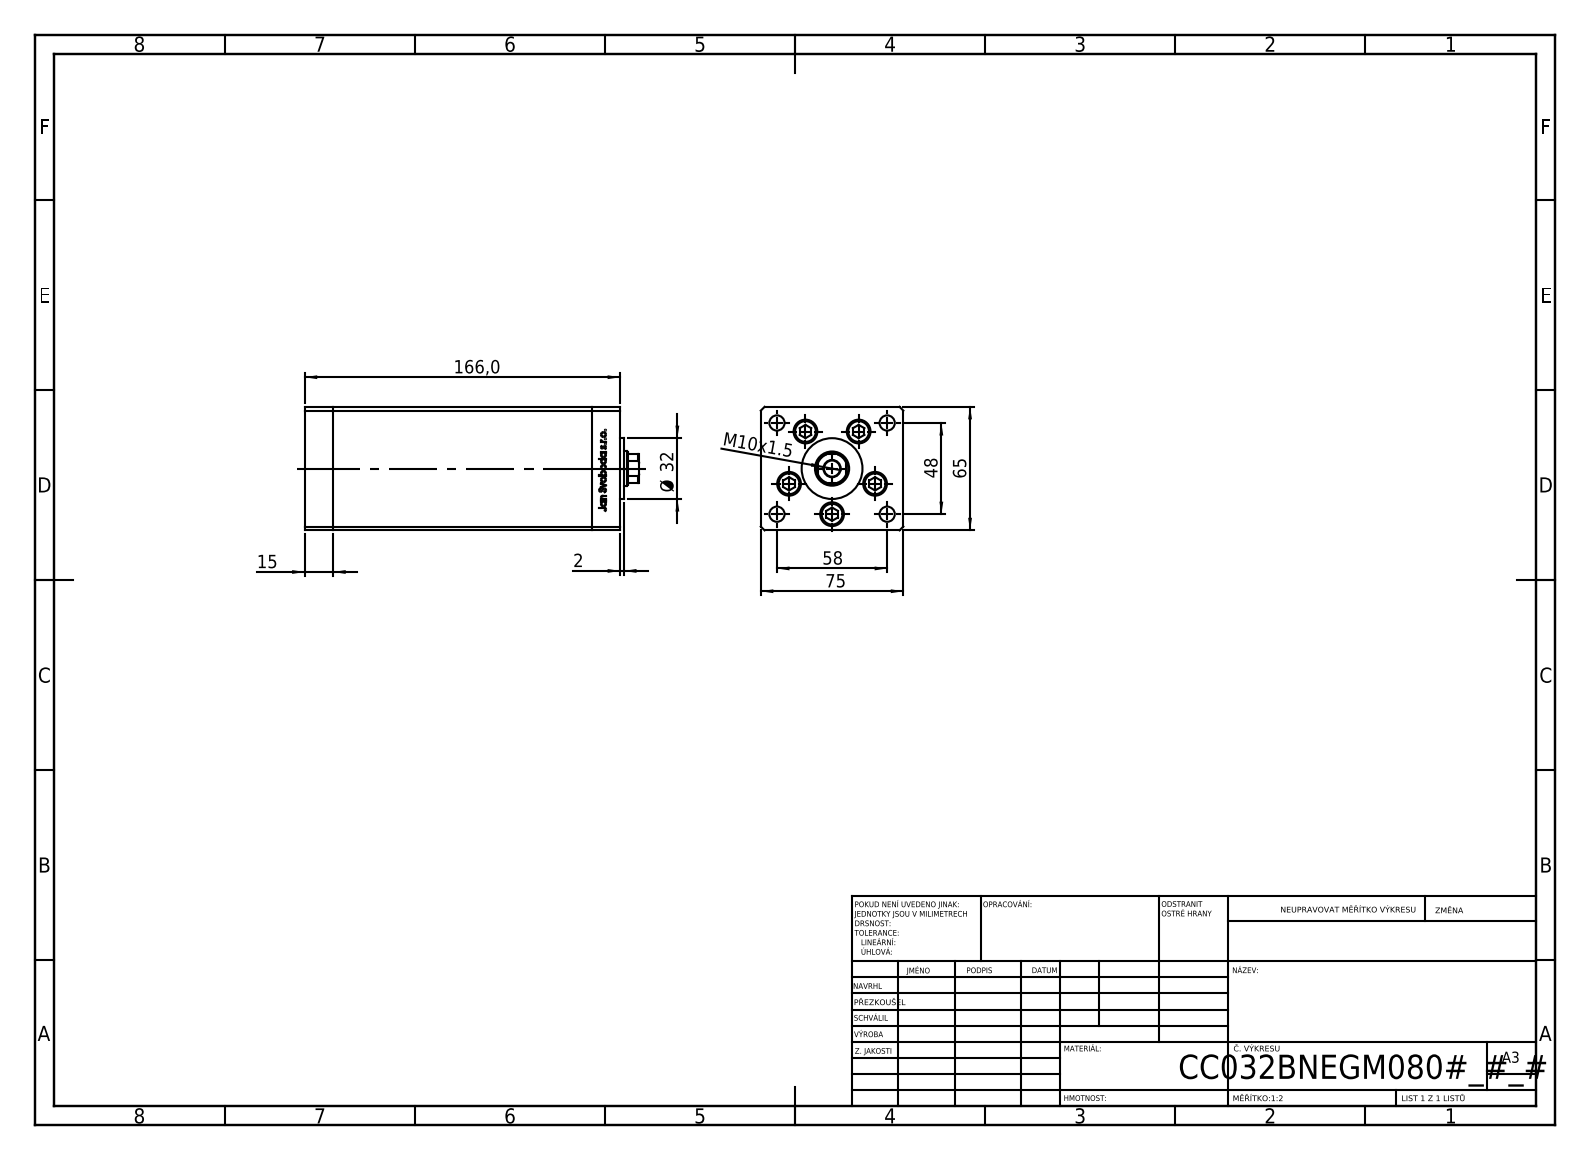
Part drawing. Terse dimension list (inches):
name: V220C_B MIDDLE; V220C_VC_B; V220C BACK_B; V220C_FRONT_B (+1 more)
written by: SolidWorks 2019 (CONFIG_CONTROL_DESIGN)
unit: in
bodies: 14 solids, 1183 faces (462 planar, 147 cylindrical, 574 other)
size: 6.929 × 2.953 × 2.559
volume: 44.09 in³; area: 197.4 in²
holes: 5× ⌀0.354, 5× ⌀0.492, 4× ⌀0.315, 2× ⌀0.079, 2× ⌀0.518, 1× ⌀0.335, 1× ⌀0.709
bosses: 5× ⌀0.315, 1× ⌀1.26
rounds: 2× R0.037, 1× R0.335
face distances: 2.953, 2.559, 0.591, 5.354, 5.945, 6.535, 1.102, 0.512, 2.146, 0.413
hole spacings: 0.945, 1.482, 0.617, 0.678, 1.091, 1.135, 1.142, 1.285
